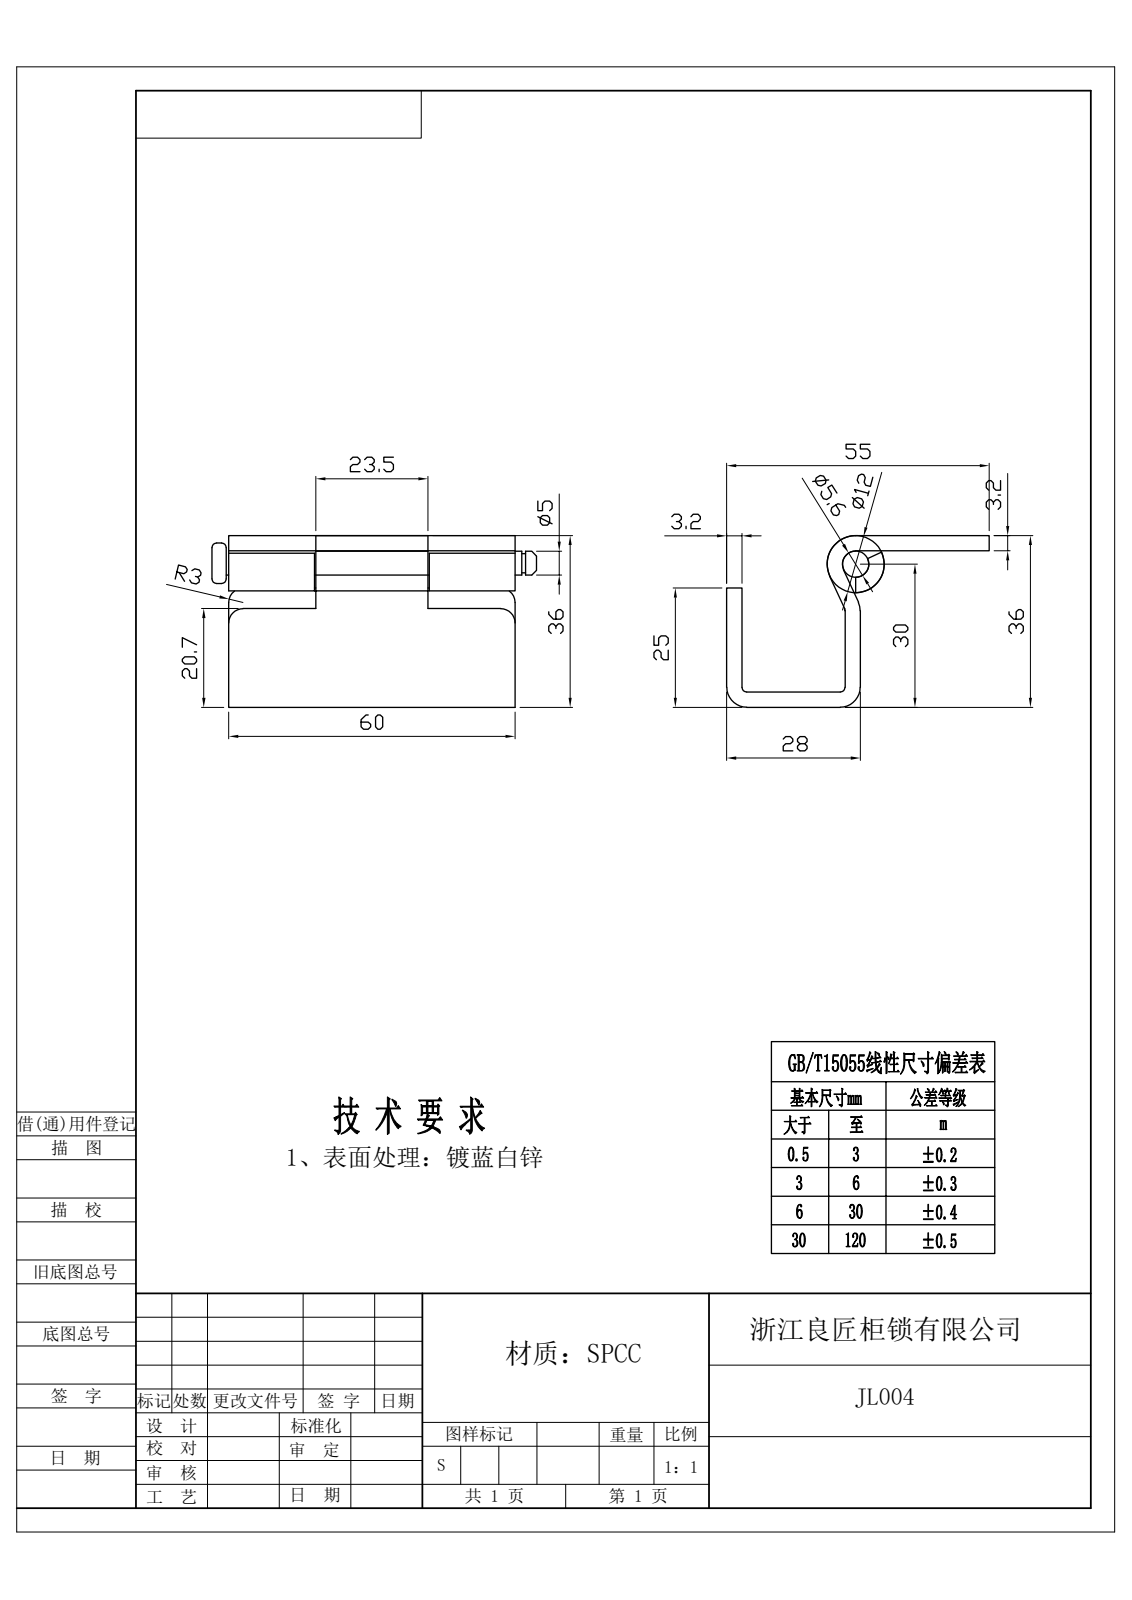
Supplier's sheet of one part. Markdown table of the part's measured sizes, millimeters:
| quantity | value |
| --- | --- |
| STEP written by | Rhino 8.5 (CONFIG_CONTROL_DESIGN) |
| units | millimeters |
| bodies | 9 solids, 76 faces (42 planar, 28 cylindrical, 6 other) |
| overall size | 66.7 × 55 × 36 |
| volume | 24 167 mm³ |
| surface area | 17 584 mm² |
| round holes (diameter × count) | 5.6 × 1 |
| round bosses / shafts (diameter × count) | 12 × 1, 8.5 × 1, 5 × 1, 4 × 1 |
| partial cylindrical surfaces (radius × count) | 3 × 6, 1 × 2, 4.2 × 2 |
| main face-to-face distances | 3.2, 32.8, 24.8, 36, 29.6, 21.6, 28, 60, 18.25, 41.75 |
